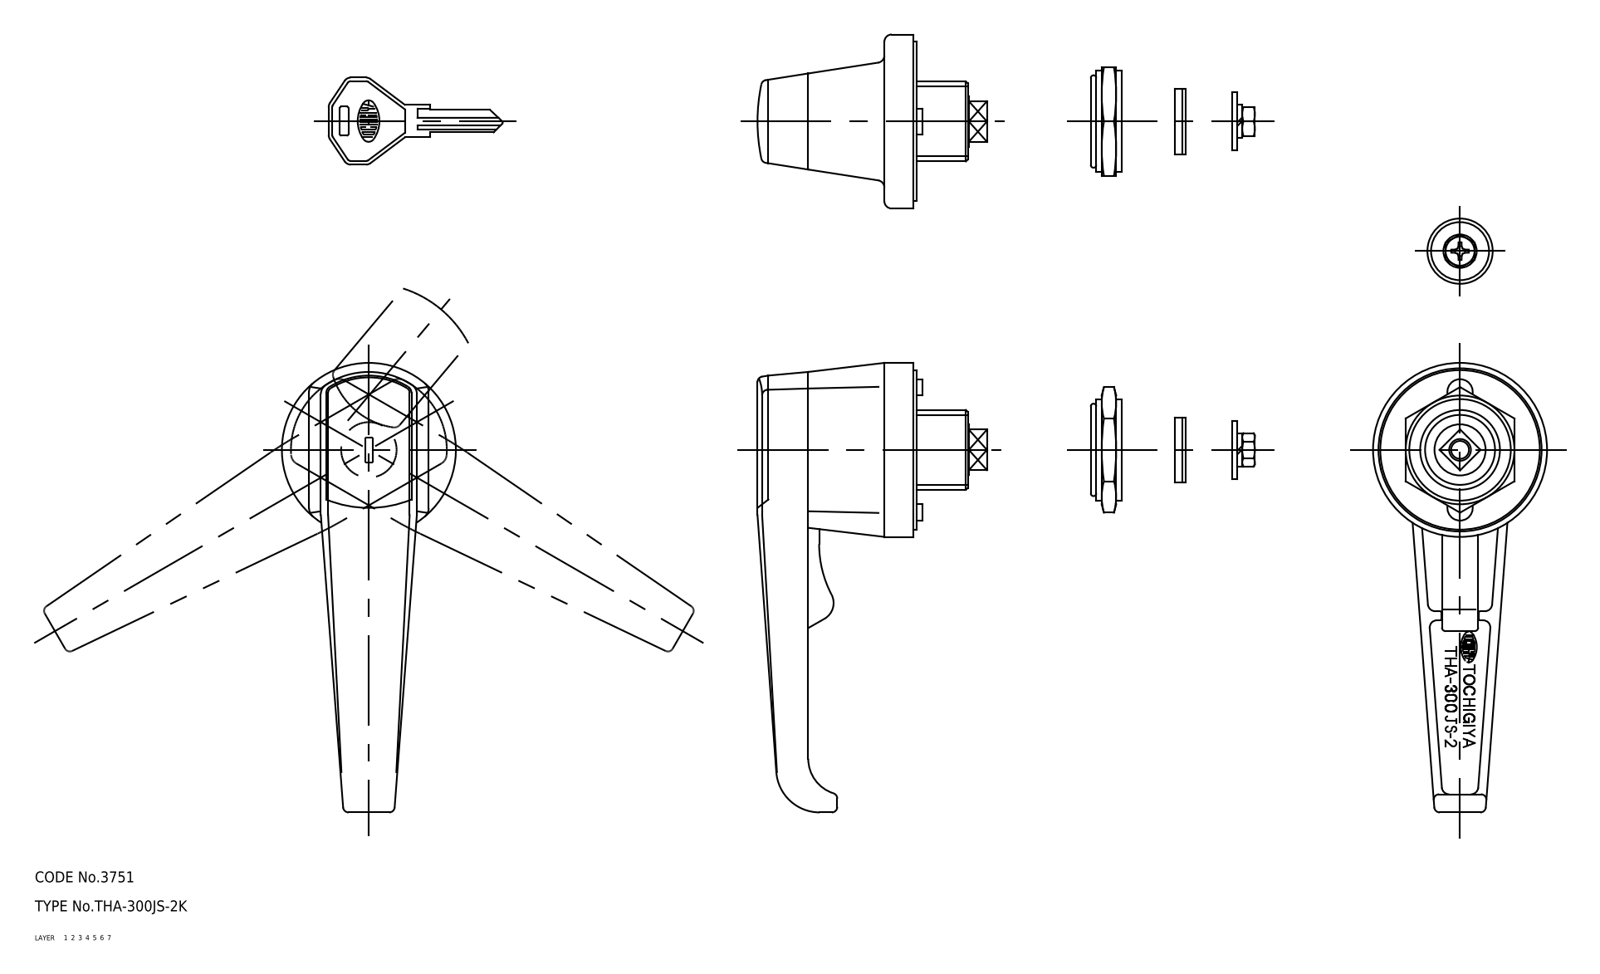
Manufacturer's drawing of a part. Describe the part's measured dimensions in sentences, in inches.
The part is named "cap; washer_D; washer_B; washer_A (+8 more)". Its 3-D file was written by "CADfix (AUTOMOTIVE_DESIGN)". It is 12 solids with 431 faces: 0 planar, 0 cylindrical and 431 other. Overall it measures 5.471 by 4.882 by 1.89 inches. Its volume is 3.351 cubic inches and its surface area 62.38 square inches.
